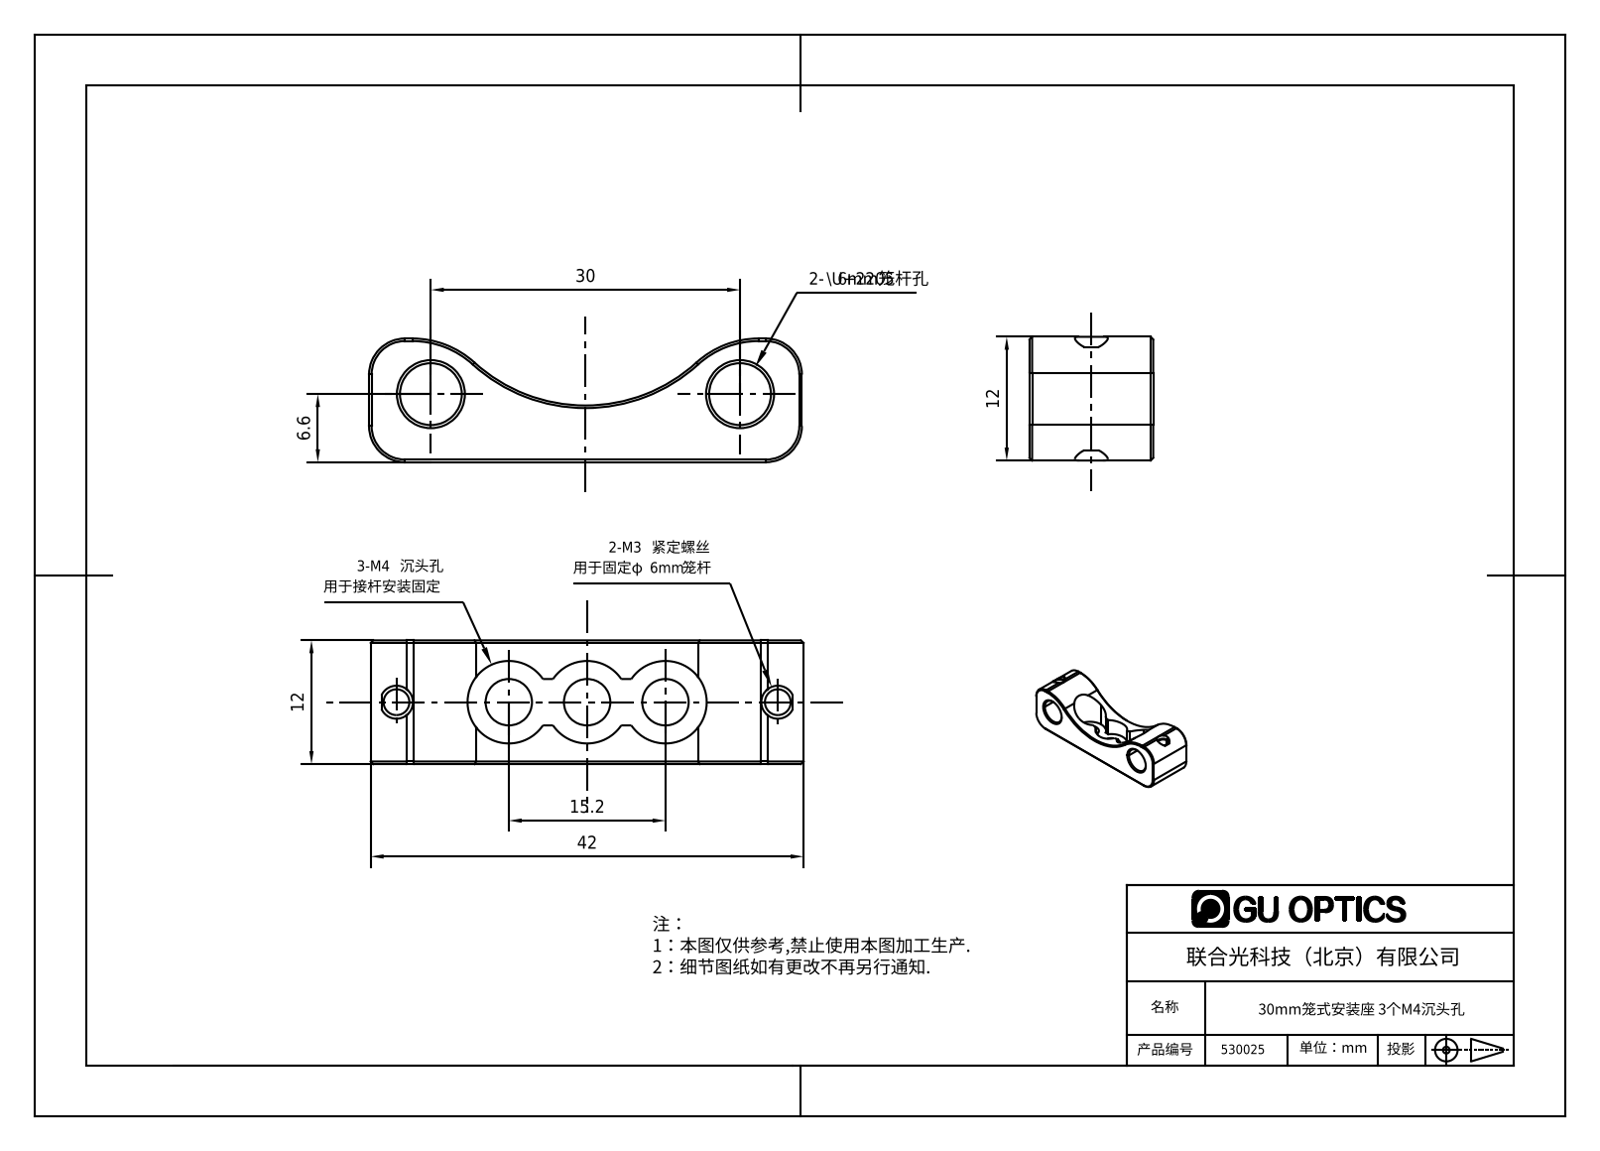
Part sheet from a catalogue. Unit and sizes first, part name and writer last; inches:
Units: inches
Overall size (bounding box): 1.654 × 0.472 × 0.472
Round holes (diameter × count): ⌀0.177 ×3, ⌀0.098 ×2, ⌀0.126 ×2, ⌀0.236 ×2, ⌀0.315 ×2
Round bosses / shafts (diameter × count): ⌀0.118 ×2
Partial cylindrical surfaces — rounded edges, fillets, slot ends (radius × count): R0.138 ×4, R0.354 ×2, R0.157 ×1, R0.63 ×1
Main face-to-face distances: 0.472, 0.059, 1.654, 0.148, 0.325, 0.413, 0.039, 0.433, 0.177, 0.02
Hole centre spacings: 0.299, 0.429, 0.728, 1.028, 0.598, 1.181, 1.457
Bodies: 0 solids, 125 faces (40 planar, 47 cylindrical, 38 other)
Part name (STEP PRODUCT): 2.4.4.3_LZA-B30_30mm笼式系统支杆安装座,，带3个M4沉头孔
STEP written by: SolidWorks 2018 (AUTOMOTIVE_DESIGN)
